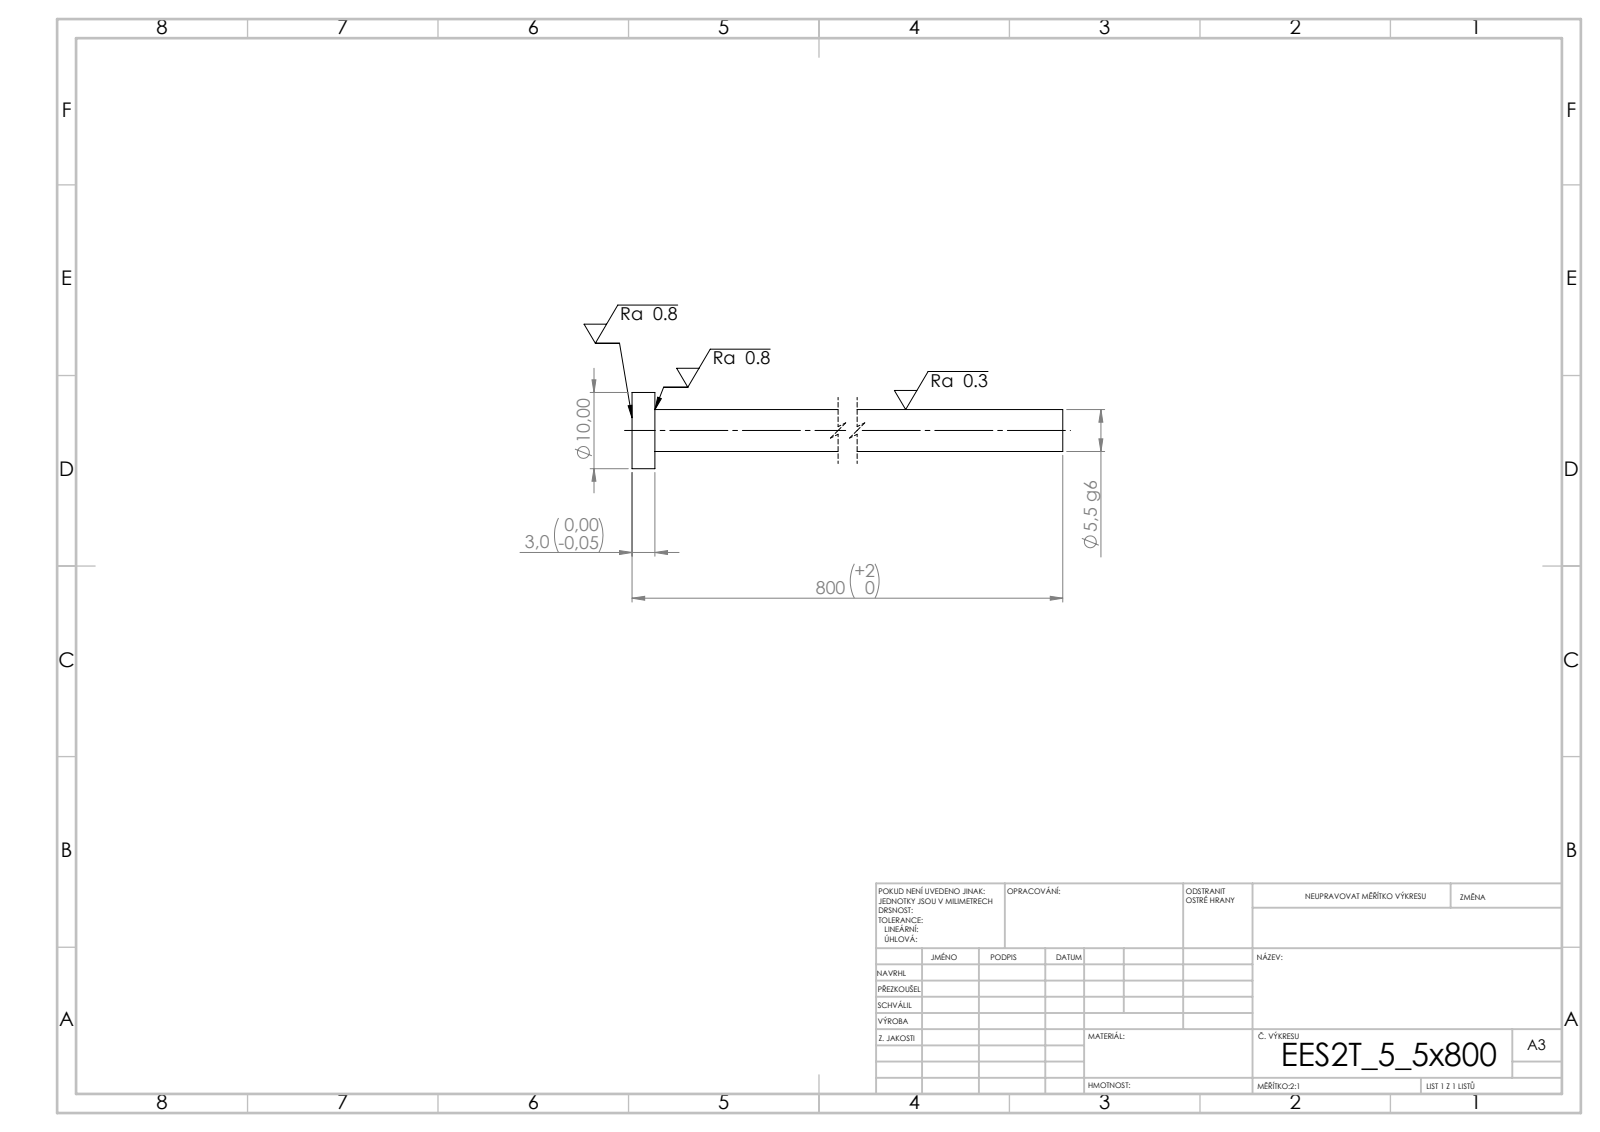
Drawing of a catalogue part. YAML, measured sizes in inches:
step_written_by: "SolidWorks 2019 (CONFIG_CONTROL_DESIGN)"
units: inches
bodies: {solids: 1, faces: 7, planar: 3, cylindrical: 4, other: 0}
overall_size: [31.496, 0.394, 0.394]
volume: 1.17
surface_area: 21.73
round_bosses_or_shafts:
  - {diameter: 0.394, count: 1}
  - {diameter: 0.217, count: 1}
face_to_face_distances: [0.118, 31.496, 31.378]
